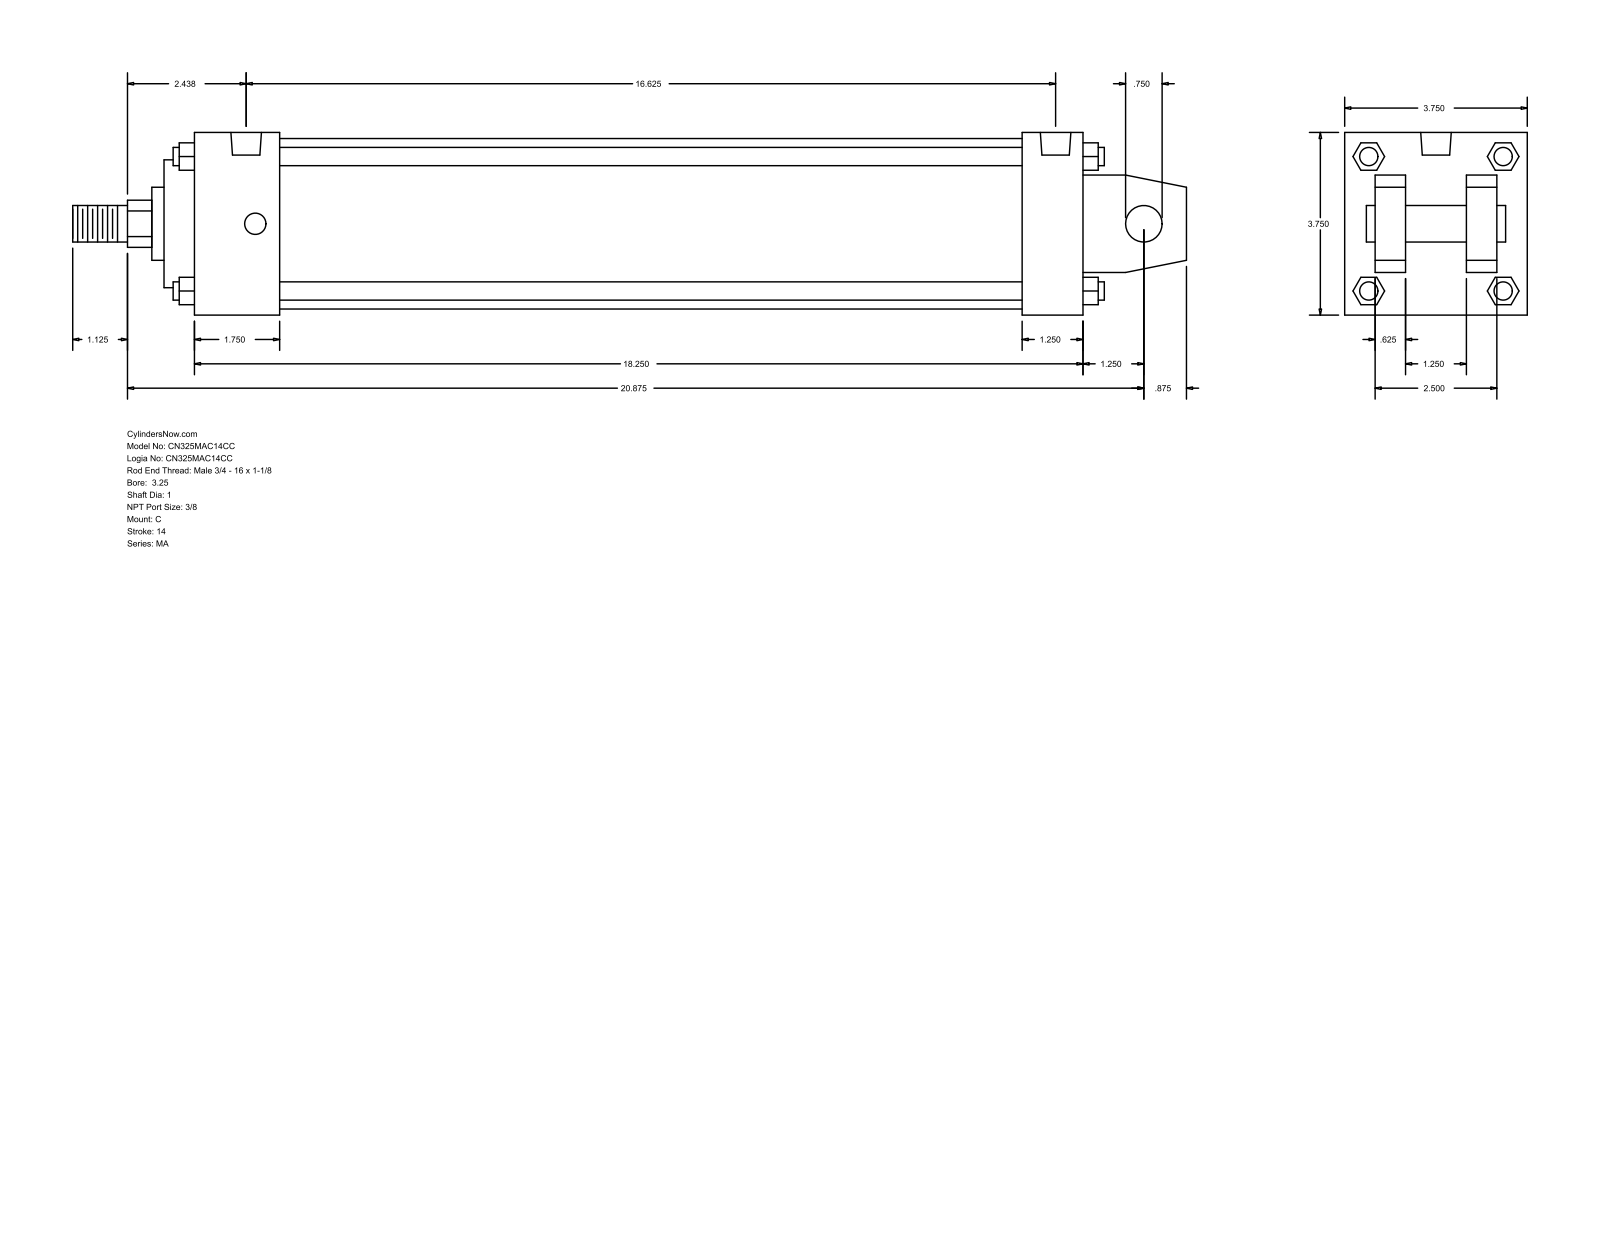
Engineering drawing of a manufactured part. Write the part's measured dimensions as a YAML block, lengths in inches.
part_name: "MA_C__0325_1"
step_written_by: "GSSL Pune (CONFIG_CONTROL_DESIGN)"
units: inches
bodies: {solids: 0, faces: 141, planar: 109, cylindrical: 32, other: 0}
overall_size: [22.875, 3.75, 3.75]
round_holes:
  - {diameter: 0.437, count: 4}
  - {diameter: 0.627, count: 2}
round_bosses_or_shafts:
  - {diameter: 0.375, count: 4}
  - {diameter: 0.75, count: 2}
  - {diameter: 3.5, count: 1}
  - {diameter: 2.625, count: 1}
  - {diameter: 1.5, count: 1}
  - {diameter: 1, count: 1}
partial_cylinders:
  - {radius: 0.484, count: 1}
face_to_face_distances: [3.75, 0.625, 2.5, 18.25, 1.25, 3.125, 1.875, 17, 1.25, 1.75]
hole_center_spacings: [0.187, 16.25, 16.438, 16.625]
